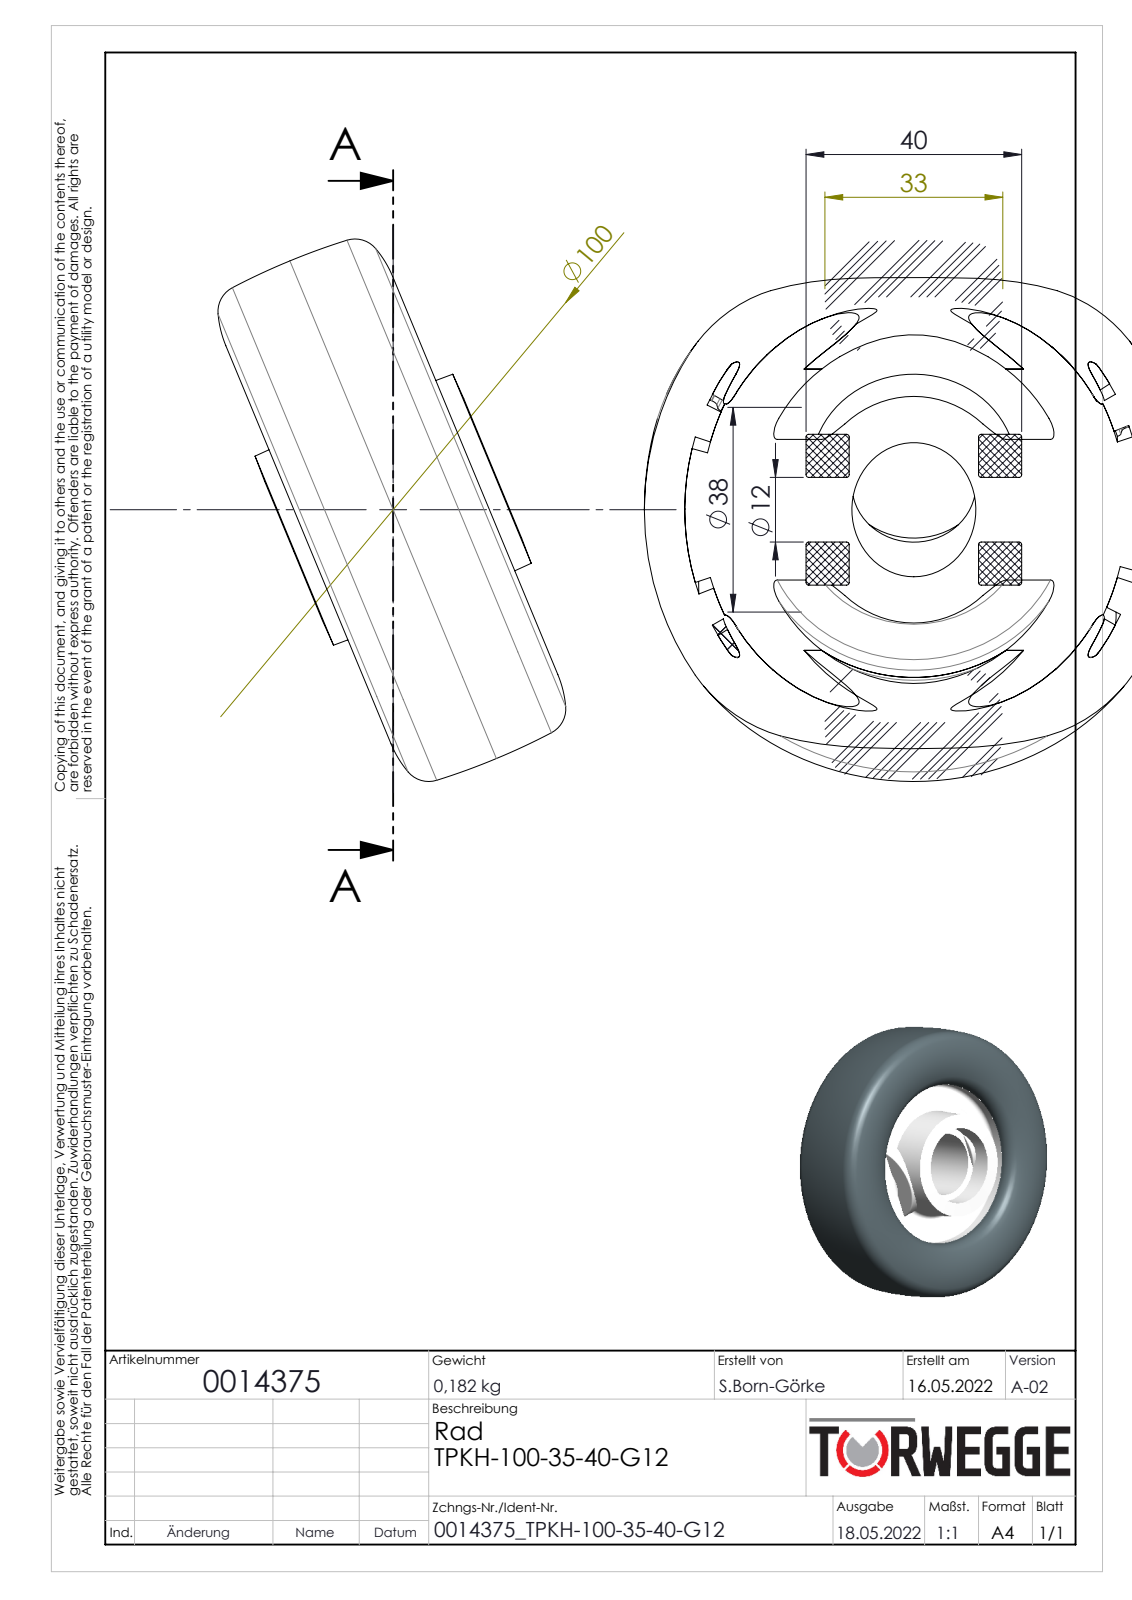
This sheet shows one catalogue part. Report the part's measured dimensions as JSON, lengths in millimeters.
{"part_name": "0014375", "step_written_by": "SolidWorks 2020 (AUTOMOTIVE_DESIGN)", "units": "millimeters", "bodies": {"solids": 0, "faces": 66, "planar": 6, "cylindrical": 10, "other": 50}, "overall_size": [100, 100, 40], "round_holes": [[12, 1], [23, 1], [59.12, 1]], "face_to_face_distances": [10, 15, 25, 30, 5, 40, 20]}
